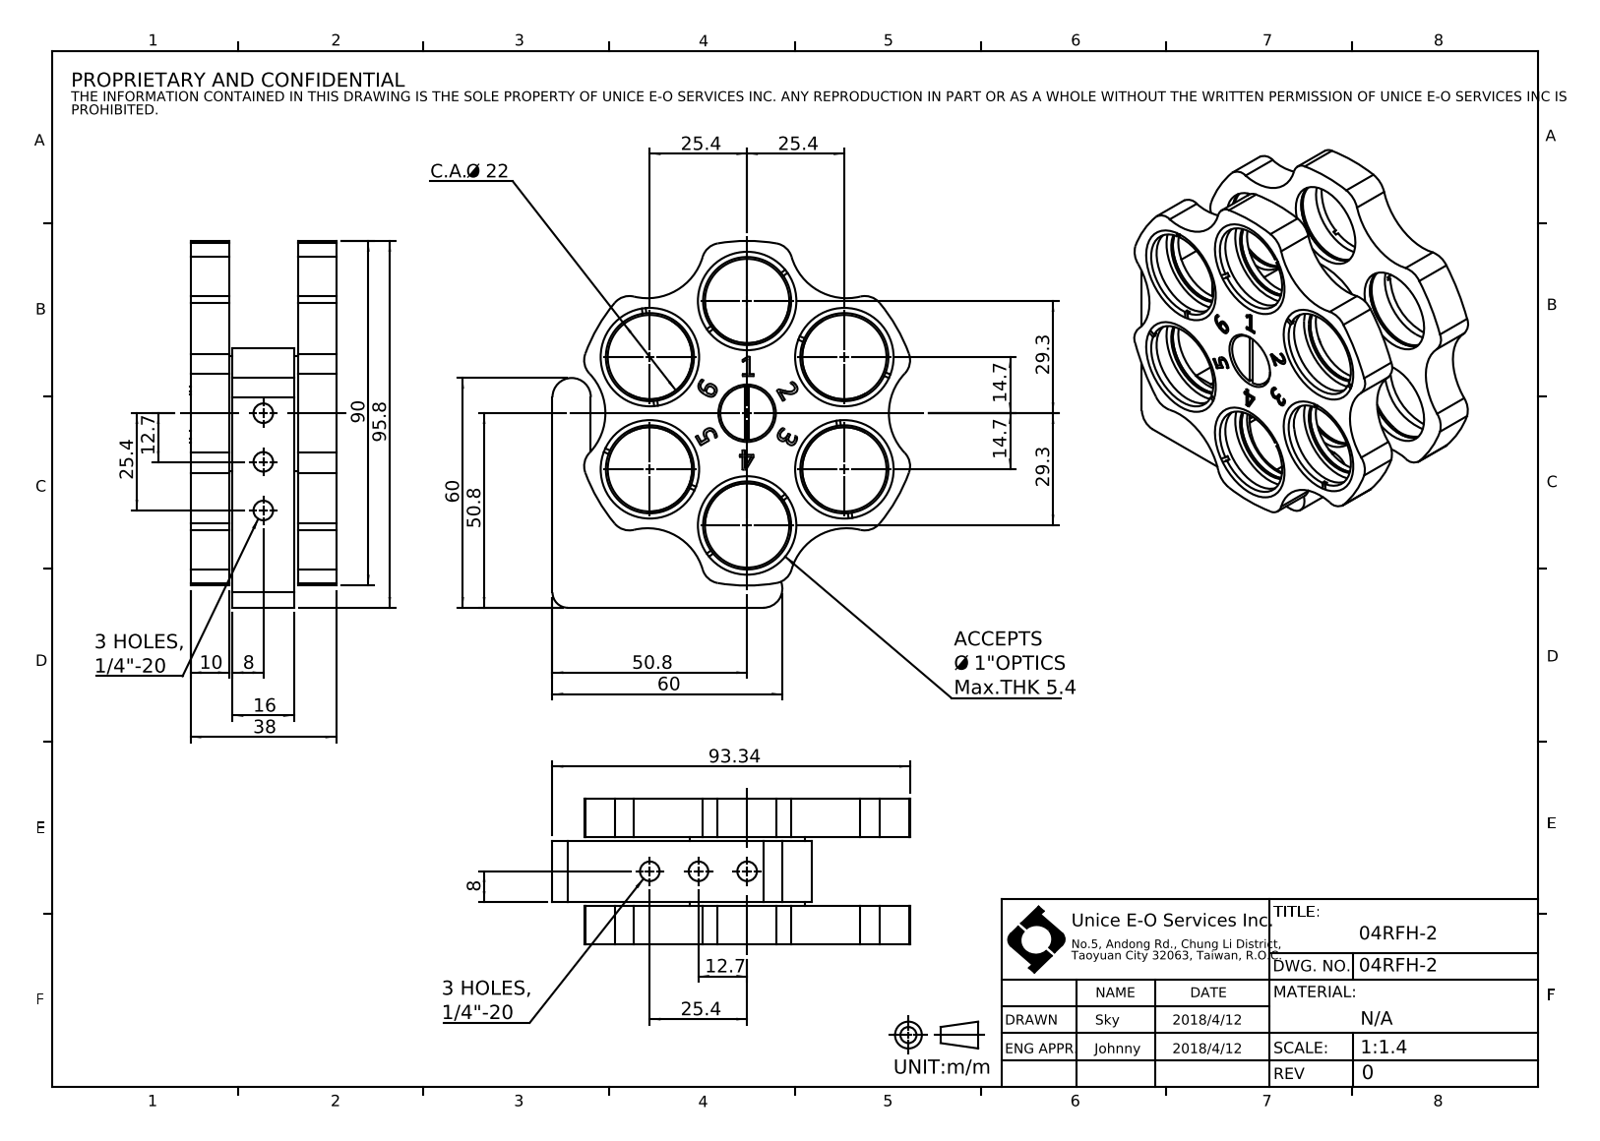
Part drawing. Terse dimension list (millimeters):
name: 04RFH-2
written by: SolidWorks 2016 (CONFIG_CONTROL_DESIGN)
unit: mm
bodies: 30 solids, 648 faces (171 planar, 320 cylindrical, 157 other)
size: 95.8 × 93.34 × 38
volume: 97 822 mm³; area: 60 073 mm²
holes: 24× ⌀1.5, 12× ⌀19.5, 12× ⌀22, 6× ⌀5.11, 6× ⌀26.3, 4× ⌀5, 1× ⌀7, 1× ⌀10, 1× ⌀15
bosses: 12× ⌀25, 6× ⌀26.3, 1× ⌀30, 1× ⌀14, 1× ⌀6, 1× ⌀5
rounds: 14× R5, 6× R15, 2× R10, 2× R11, 2× R20, 1× R2.5, 1× R4, 1× R17
face distances: 27, 1, 11, 10, 28, 17, 8, 3, 7, 24
hole spacings: 29.3, 11, 31.66, 50.75, 58.6, 18.54, 19.84, 23.87
